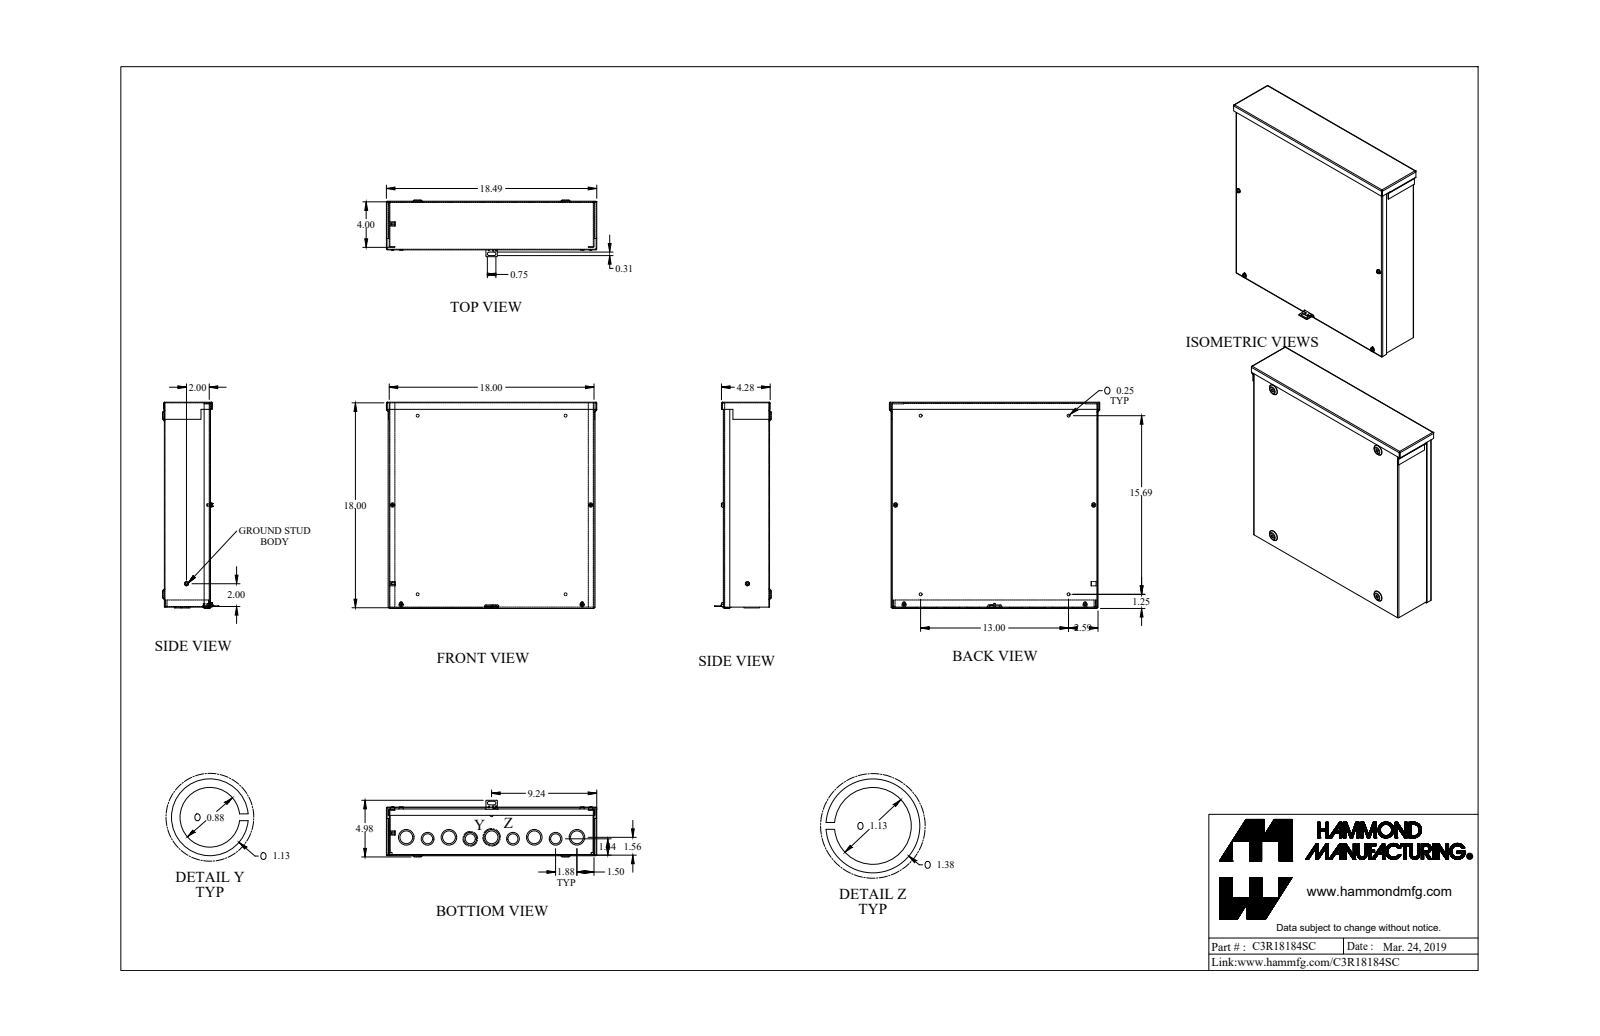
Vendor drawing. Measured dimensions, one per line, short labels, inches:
name: C3R18184SC_Default
written by: SolidWorks 2019 (CONFIG_CONTROL_DESIGN)
unit: in
bodies: 11 solids, 457 faces (238 planar, 133 cylindrical, 86 other)
size: 18.489 × 18.12 × 4.977
volume: 59.77 in³; area: 2 107 in²
holes: 4× ⌀0.17, 4× ⌀0.25, 4× ⌀0.875, 3× ⌀1.125, 2× ⌀1.125, 1× ⌀0.125, 1× ⌀0.137, 1× ⌀0.156
bosses: 4× ⌀1.125, 4× ⌀0.19, 3× ⌀1.375, 3× ⌀0.375, 2× ⌀1.375, 2× ⌀0.375, 1× ⌀0.125
rounds: 21× R0.029, 21× R0.086, 8× R0.109, 8× R0.125, 2× R0.156
face distances: 0.057, 4, 3.943, 4.057, 17.943, 18, 0.057, 17.886, 17.886, 17.943
hole spacings: 7.5, 1.879, 1.88, 3.75, 5.627, 8.151, 17.112, 1.688
